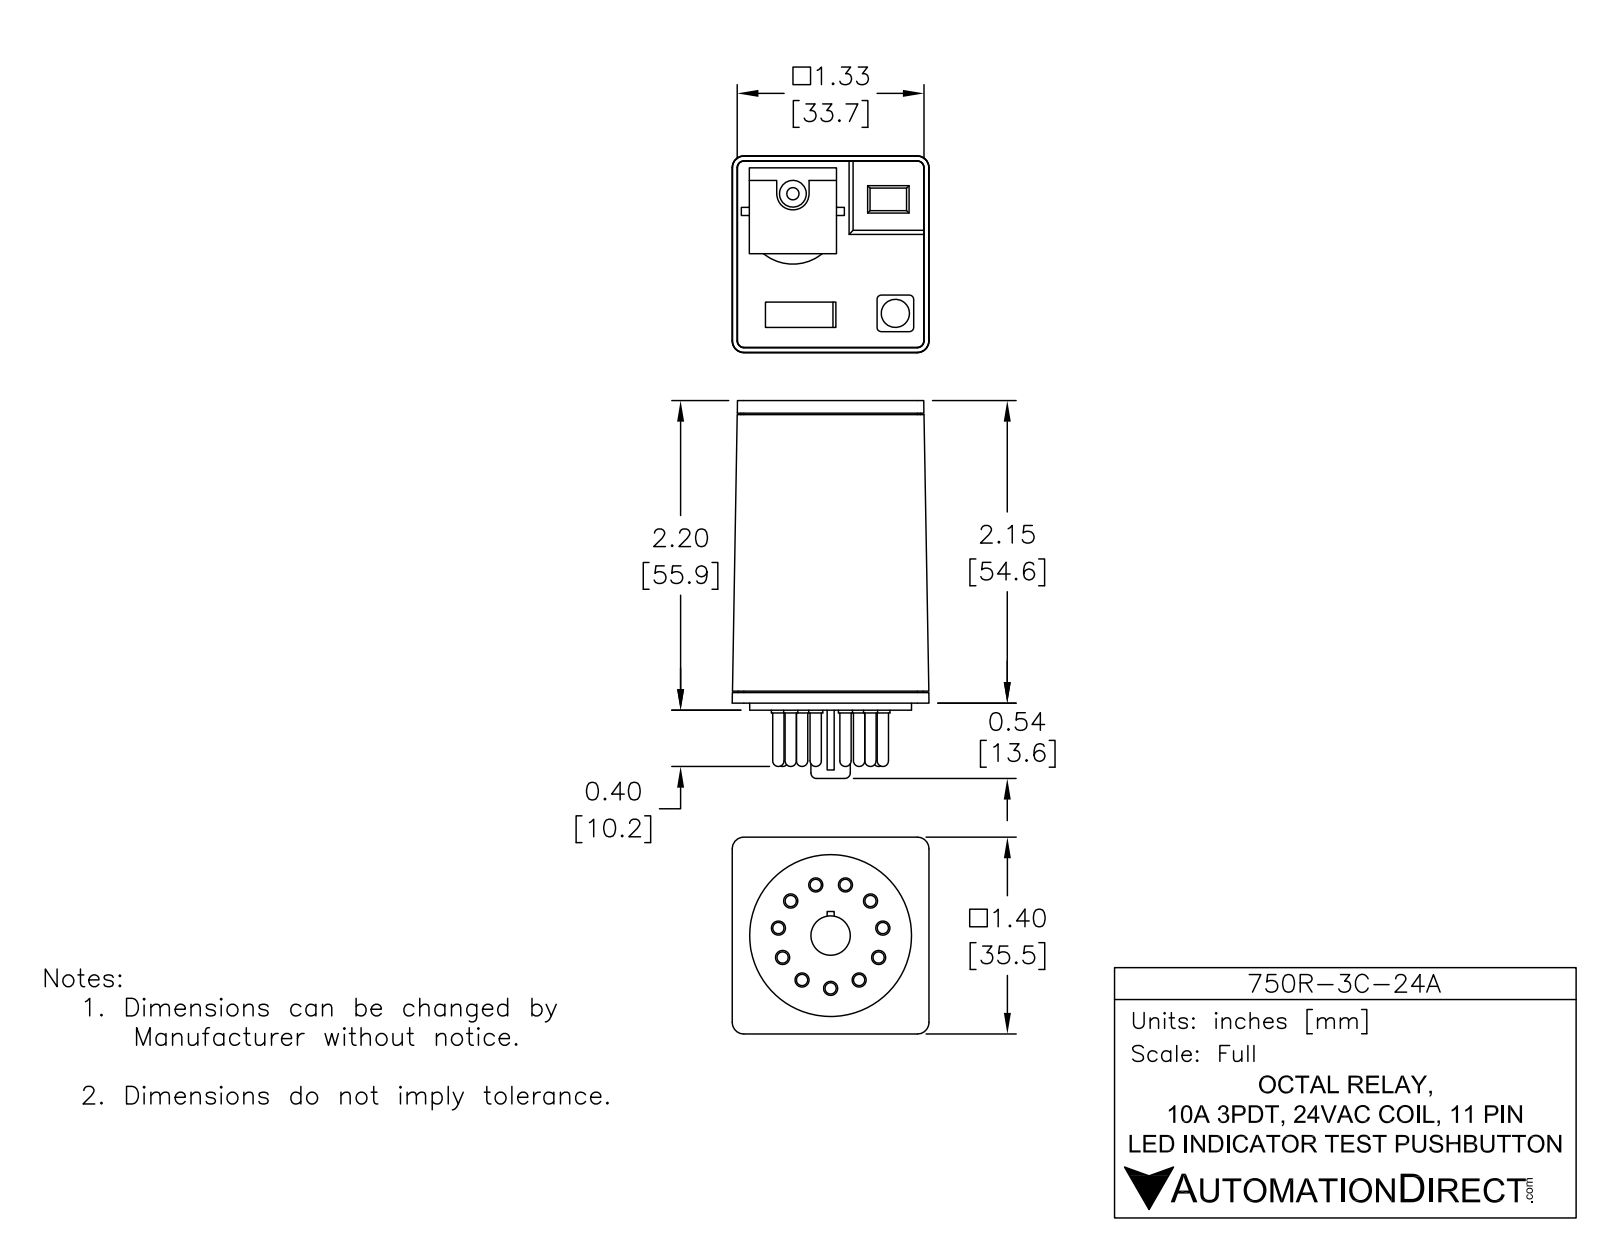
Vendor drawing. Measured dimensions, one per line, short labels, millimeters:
name: 750R-3C-24A
written by: SolidWorks 2014 (AUTOMOTIVE_DESIGN)
unit: mm
bodies: 1 solid, 180 faces (93 planar, 62 cylindrical, 25 other)
size: 68.2 × 35.5 × 35.5
volume: 66 470 mm³; area: 11 410 mm²
holes: 1× ⌀2.2, 1× ⌀5.1
bosses: 11× ⌀2.5, 11× ⌀2, 1× ⌀29.2, 1× ⌀7.1, 1× ⌀4.8
rounds: 4× R0.8, 1× R2.9, 1× R8.4
face distances: 1.3, 54.6, 55.9, 53.6, 1, 55.6, 54.4, 2.2, 0.8, 54.9
hole spacings: 28.4
